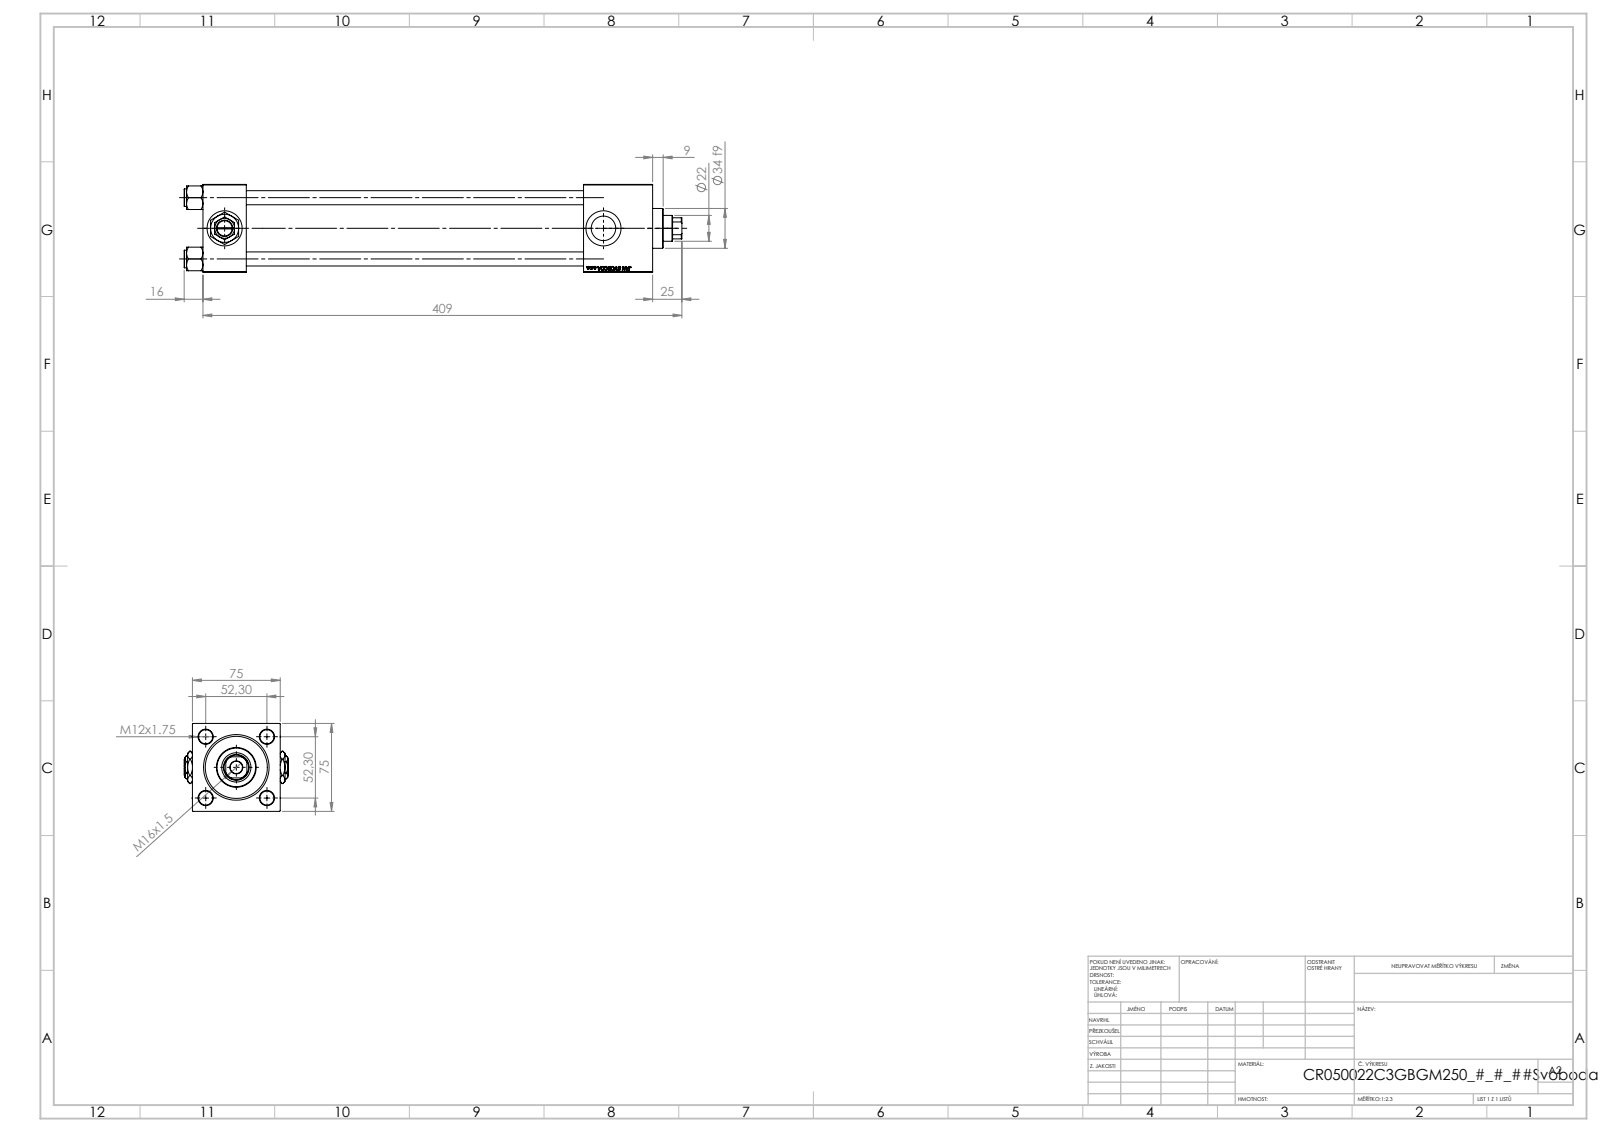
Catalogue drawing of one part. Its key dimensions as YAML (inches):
part_name: "V215_VC_A; V215CR_C_Body; Zatka_pro_OIL_PORT; NUT_M5_C (+2 more)"
step_written_by: "SolidWorks 2019 (CONFIG_CONTROL_DESIGN)"
units: inches
bodies: {solids: 13, faces: 1249, planar: 573, cylindrical: 98, other: 578}
overall_size: [16.732, 3.504, 2.953]
volume: 58.47
surface_area: 432.3
round_holes:
  - {diameter: 0.472, count: 4}
  - {diameter: 0.276, count: 2}
  - {diameter: 0.825, count: 2}
  - {diameter: 1.181, count: 2}
  - {diameter: 0.413, count: 1}
  - {diameter: 0.866, count: 1}
  - {diameter: 0.984, count: 1}
  - {diameter: 1.614, count: 1}
  - {diameter: 1.969, count: 1}
  - {diameter: 2.087, count: 1}
round_bosses_or_shafts:
  - {diameter: 0.591, count: 4}
  - {diameter: 2.205, count: 1}
  - {diameter: 1.339, count: 1}
partial_cylinders:
  - {radius: 0.413, count: 1}
face_to_face_distances: [2.953, 1.457, 15.118, 13.661, 12.795, 11.339, 2.323, 13.988, 12.531, 1.193]
hole_center_spacings: [1.456, 2.059, 2.912, 12.736]
